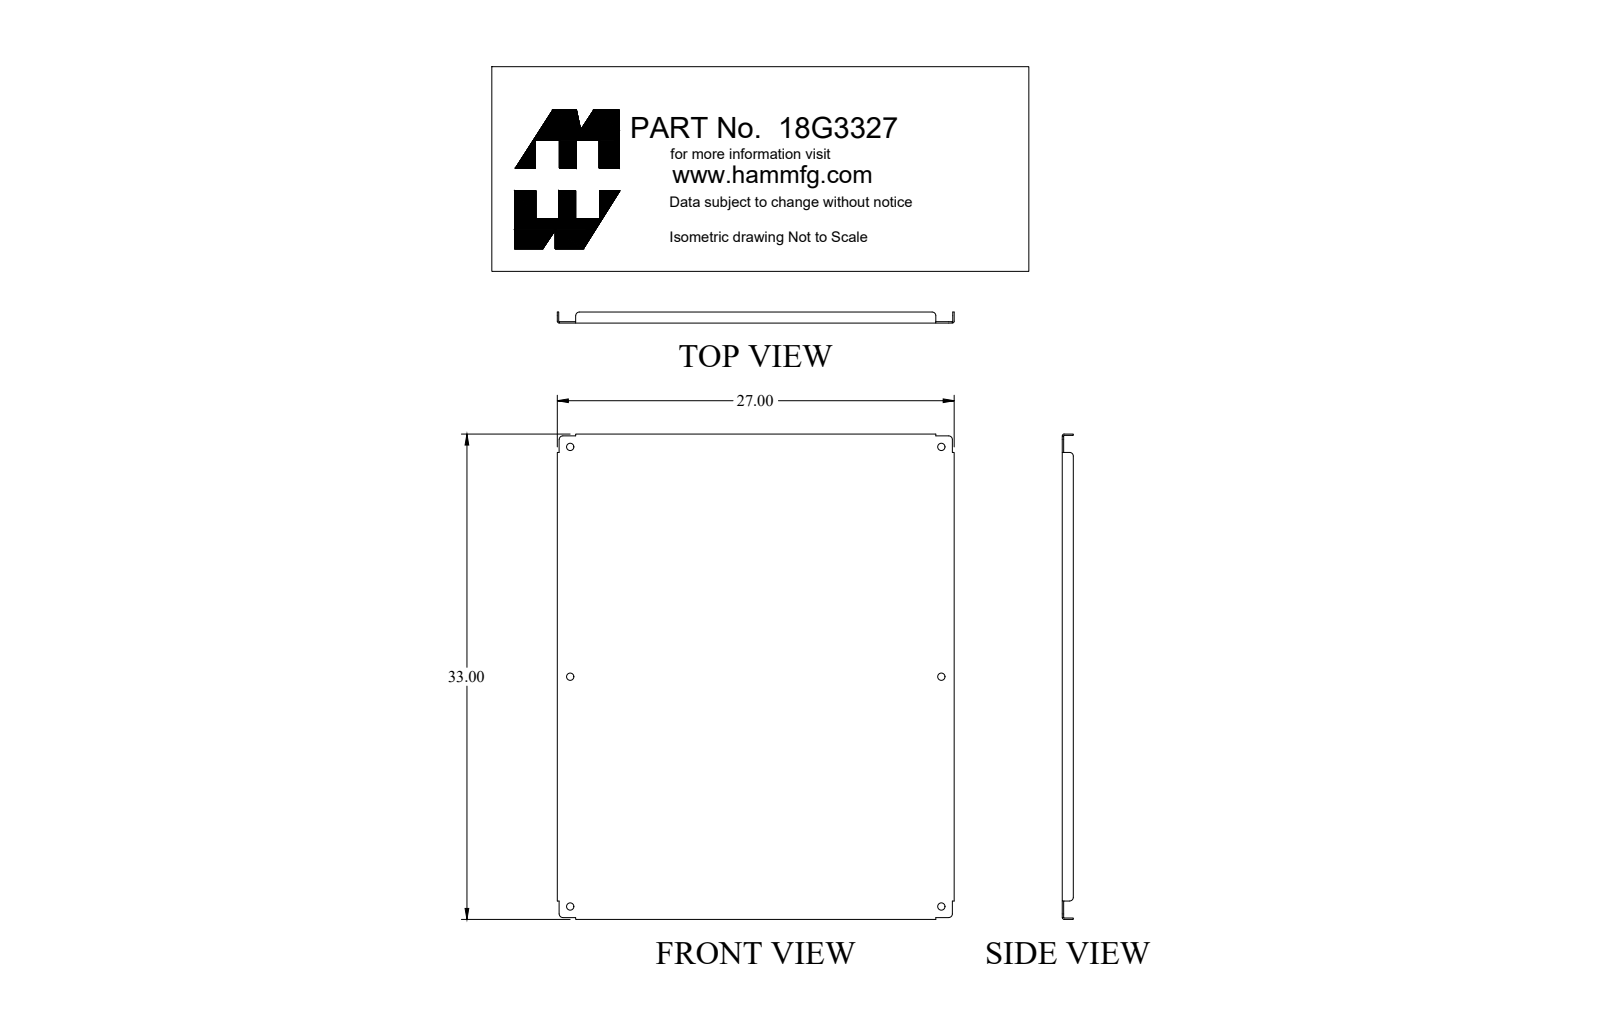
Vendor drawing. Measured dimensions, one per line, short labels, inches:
name: 18G3327_Default
written by: SolidWorks 2018 (CONFIG_CONTROL_DESIGN)
unit: in
bodies: 1 solid, 62 faces (30 planar, 32 cylindrical, 0 other)
size: 33 × 27 × 0.75
volume: 90.9 in³; area: 1 926 in²
holes: 6× ⌀0.5
rounds: 8× R0.25, 4× R0.03, 4× R0.125
face distances: 0.095, 26.905, 32.905, 26.81, 27, 33, 32.81, 0.75, 0.655, 0.125
hole spacings: 15.625, 29.693, 25.25, 31.25, 40.176
